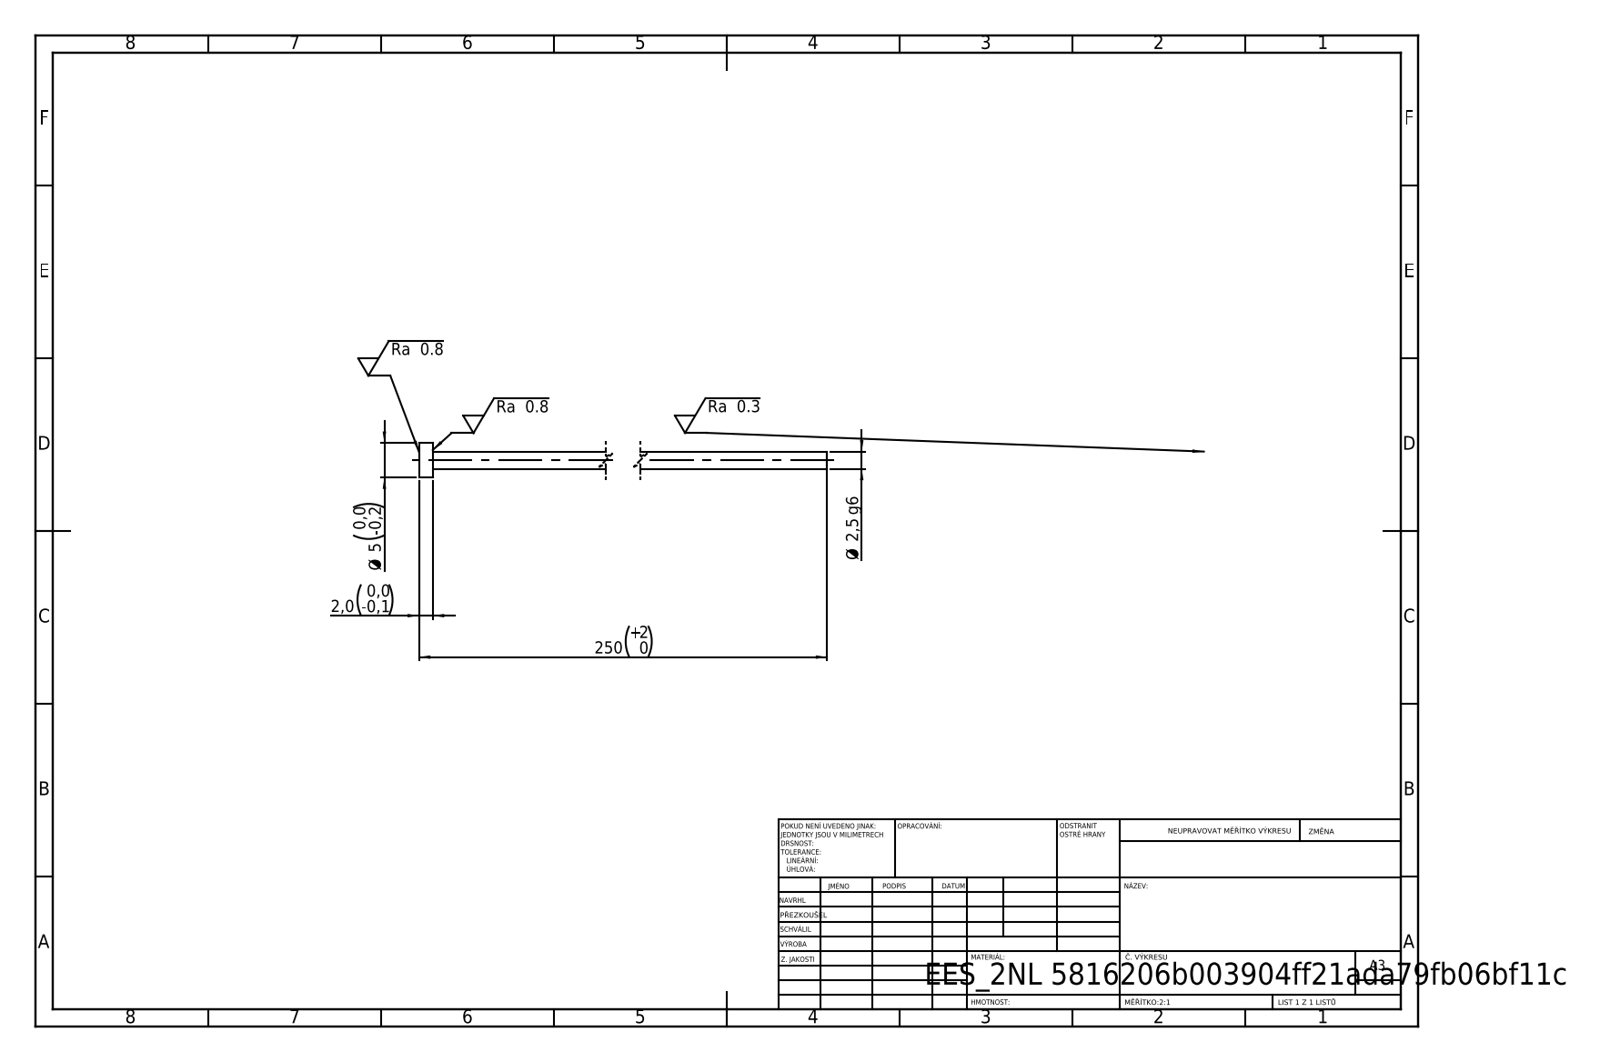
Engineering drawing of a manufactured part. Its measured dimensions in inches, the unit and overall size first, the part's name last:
Units: inches
Overall size (bounding box): 9.843 × 0.197 × 0.197
Round bosses / shafts (diameter × count): ⌀0.197 ×1, ⌀0.098 ×1
Main face-to-face distances: 0.079, 9.843, 9.764
Volume: 0.077 in³ · Surface area: 3.128 in²
Bodies: 1 solid, 7 faces (3 planar, 4 cylindrical, 0 other)
STEP written by: SolidWorks 2019 (CONFIG_CONTROL_DESIGN)
